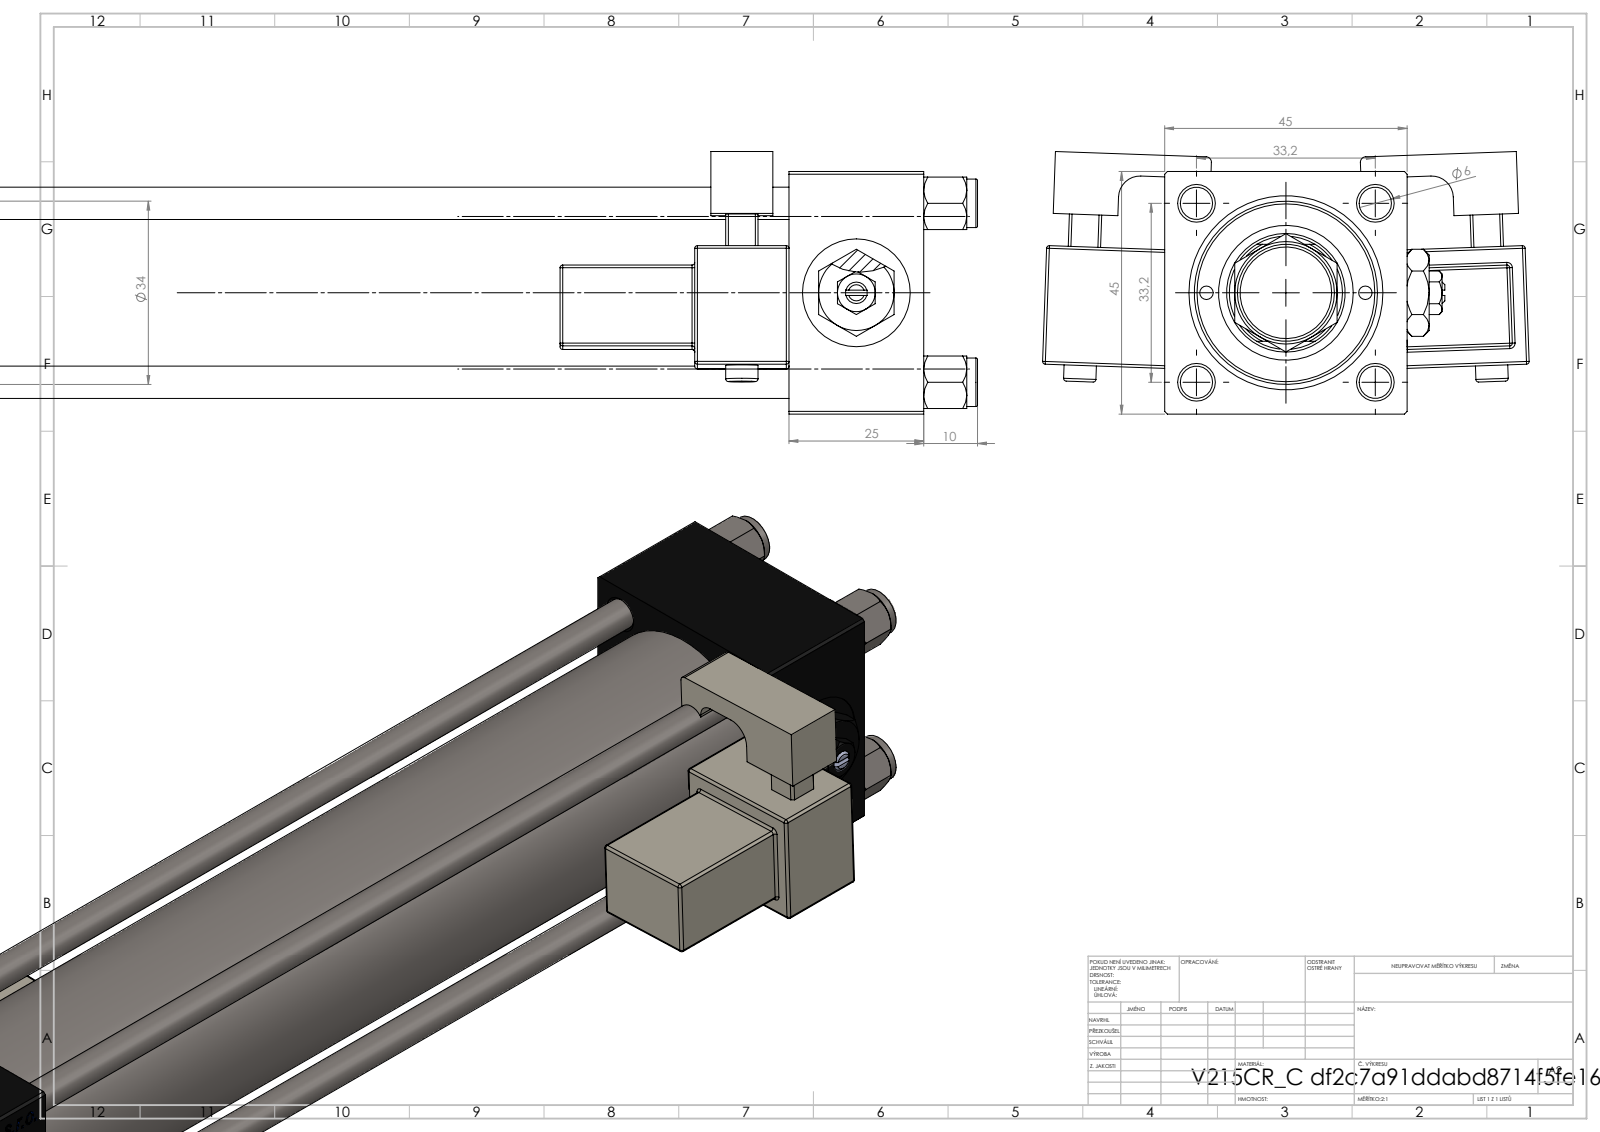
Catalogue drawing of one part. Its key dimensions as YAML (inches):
part_name: "NUT_M5_C; V215CR_C_Body; V215CR_C_TYCINKA; V215_VC_A (+4 more)"
step_written_by: "SolidWorks 2019 (CONFIG_CONTROL_DESIGN)"
units: inches
bodies: {solids: 16, faces: 1464, planar: 652, cylindrical: 166, other: 646}
overall_size: [13.031, 3.556, 1.918]
volume: 22.71
surface_area: 215.6
round_holes:
  - {diameter: 0.236, count: 4}
  - {diameter: 0.098, count: 2}
  - {diameter: 0.276, count: 2}
  - {diameter: 0.518, count: 2}
  - {diameter: 0.787, count: 2}
  - {diameter: 0.413, count: 1}
  - {diameter: 0.866, count: 1}
  - {diameter: 0.945, count: 1}
  - {diameter: 0.984, count: 1}
  - {diameter: 1.26, count: 1}
  - {diameter: 1.299, count: 1}
round_bosses_or_shafts:
  - {diameter: 0.354, count: 4}
  - {diameter: 0.236, count: 2}
  - {diameter: 1.496, count: 1}
  - {diameter: 1.339, count: 1}
  - {diameter: 0.709, count: 1}
  - {diameter: 0.433, count: 1}
partial_cylinders:
  - {radius: 0.02, count: 48}
  - {radius: 0.039, count: 2}
  - {radius: 0.098, count: 2}
  - {radius: 0.157, count: 2}
  - {radius: 0.413, count: 1}
face_to_face_distances: [1.772, 0.984, 0.118, 8.465, 7.48, 10.354, 0.905, 6.791, 9.37, 1.764]
hole_center_spacings: [0.657, 0.924, 1.307, 1.396, 0.581, 1.848, 1.161, 8.484]
